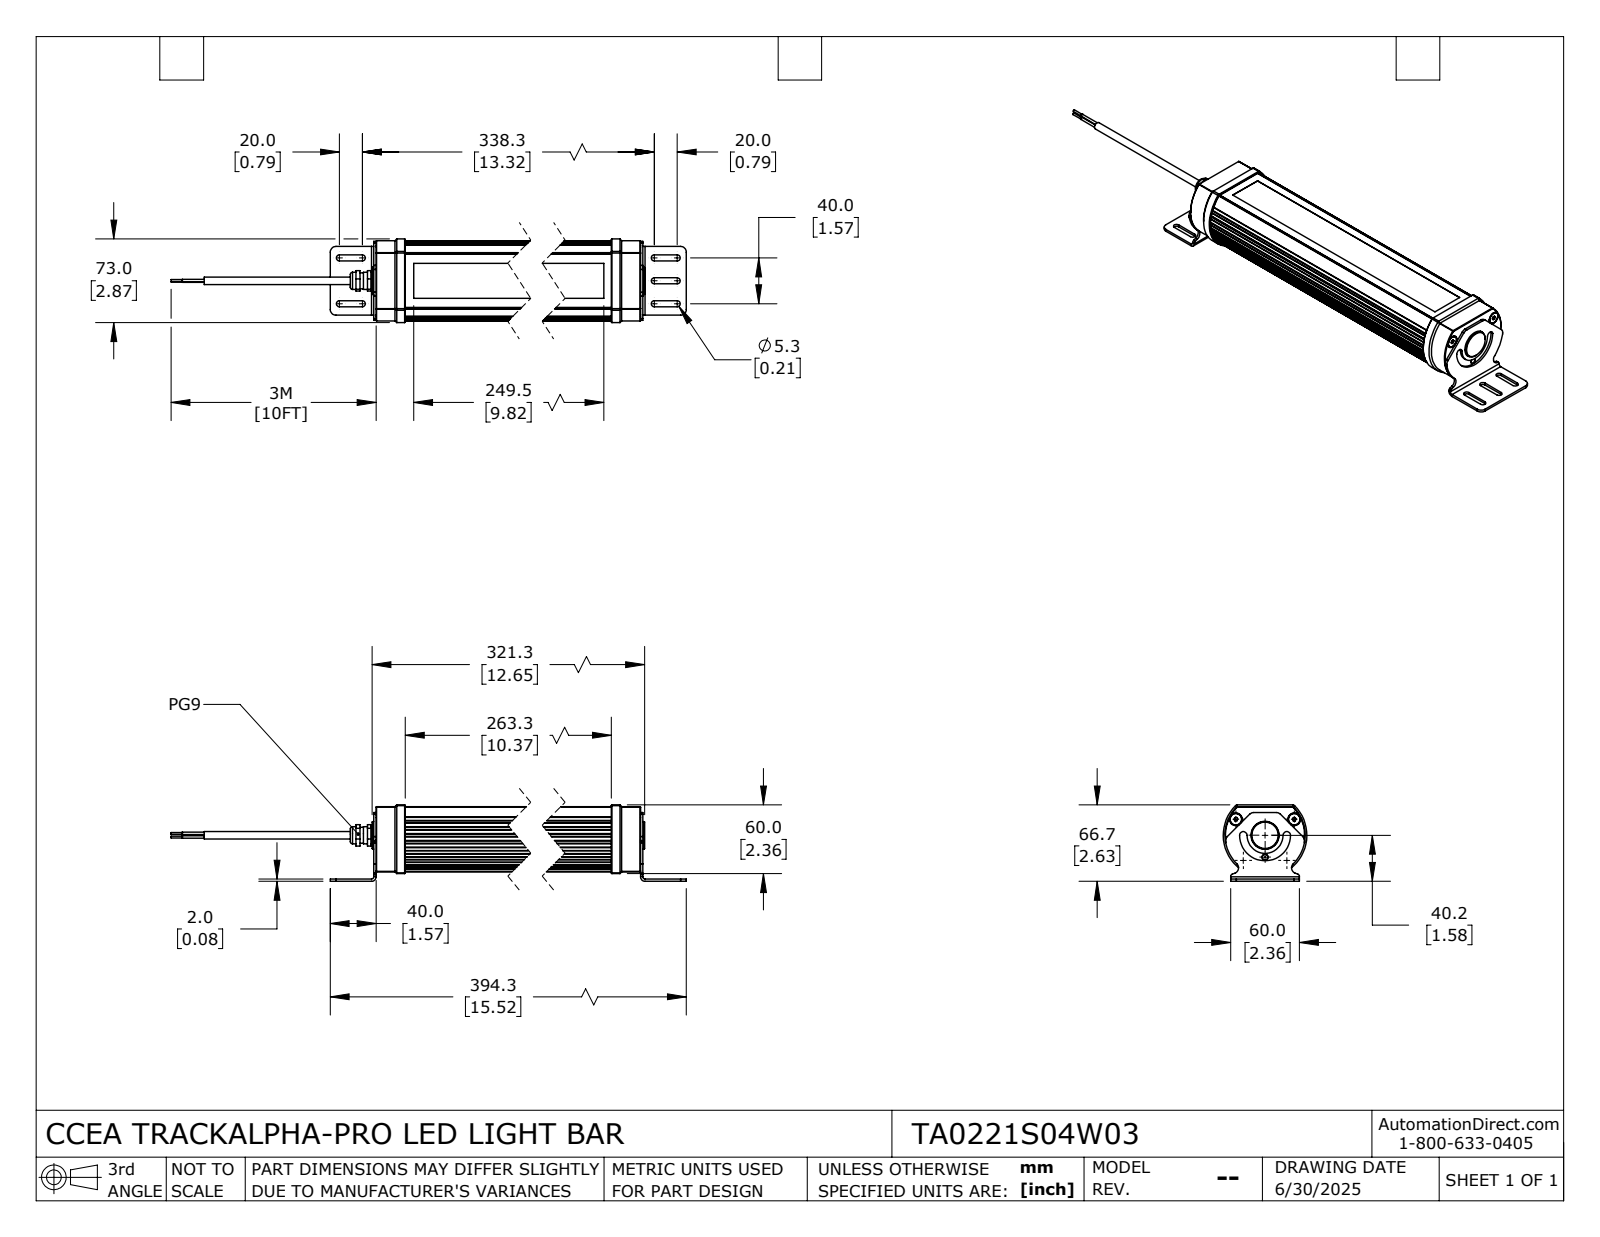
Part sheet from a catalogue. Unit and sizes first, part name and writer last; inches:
Units: inches
Overall size (bounding box): 20.996 × 2.874 × 2.626
Round holes (diameter × count): ⌀0.217 ×4, ⌀0.043 ×2, ⌀0.12 ×2, ⌀0.394 ×2, ⌀0.194 ×1, ⌀0.276 ×1, ⌀0.551 ×1, ⌀0.965 ×1, ⌀1.063 ×1
Round bosses / shafts (diameter × count): ⌀0.394 ×4, ⌀0.197 ×4, ⌀0.118 ×2, ⌀0.082 ×2, ⌀0.067 ×2, ⌀0.063 ×2, ⌀0.039 ×2, ⌀0.945 ×1
Partial cylindrical surfaces — rounded edges, fillets, slot ends (radius × count): R0.02 ×22, R0.012 ×16, R0.197 ×13, R0.104 ×12, R0.059 ×10, R0.073 ×8, R0.079 ×8, R0.028 ×2
Main face-to-face distances: 0.02, 0.079, 2.024, 2.043, 0.197, 0.217, 2.24, 2.242, 0.219, 0.199
Hole centre spacings: 0.334, 0.505, 0.726, 0.757, 0.831, 0.948, 0.992, 1.144
Volume: 65.51 in³ · Surface area: 236.9 in²
Bodies: 3 solids, 695 faces (238 planar, 331 cylindrical, 126 other)
Part name (STEP PRODUCT): TA0221S04W03
STEP written by: SolidWorks 2024 (CONFIG_CONTROL_DESIGN)
